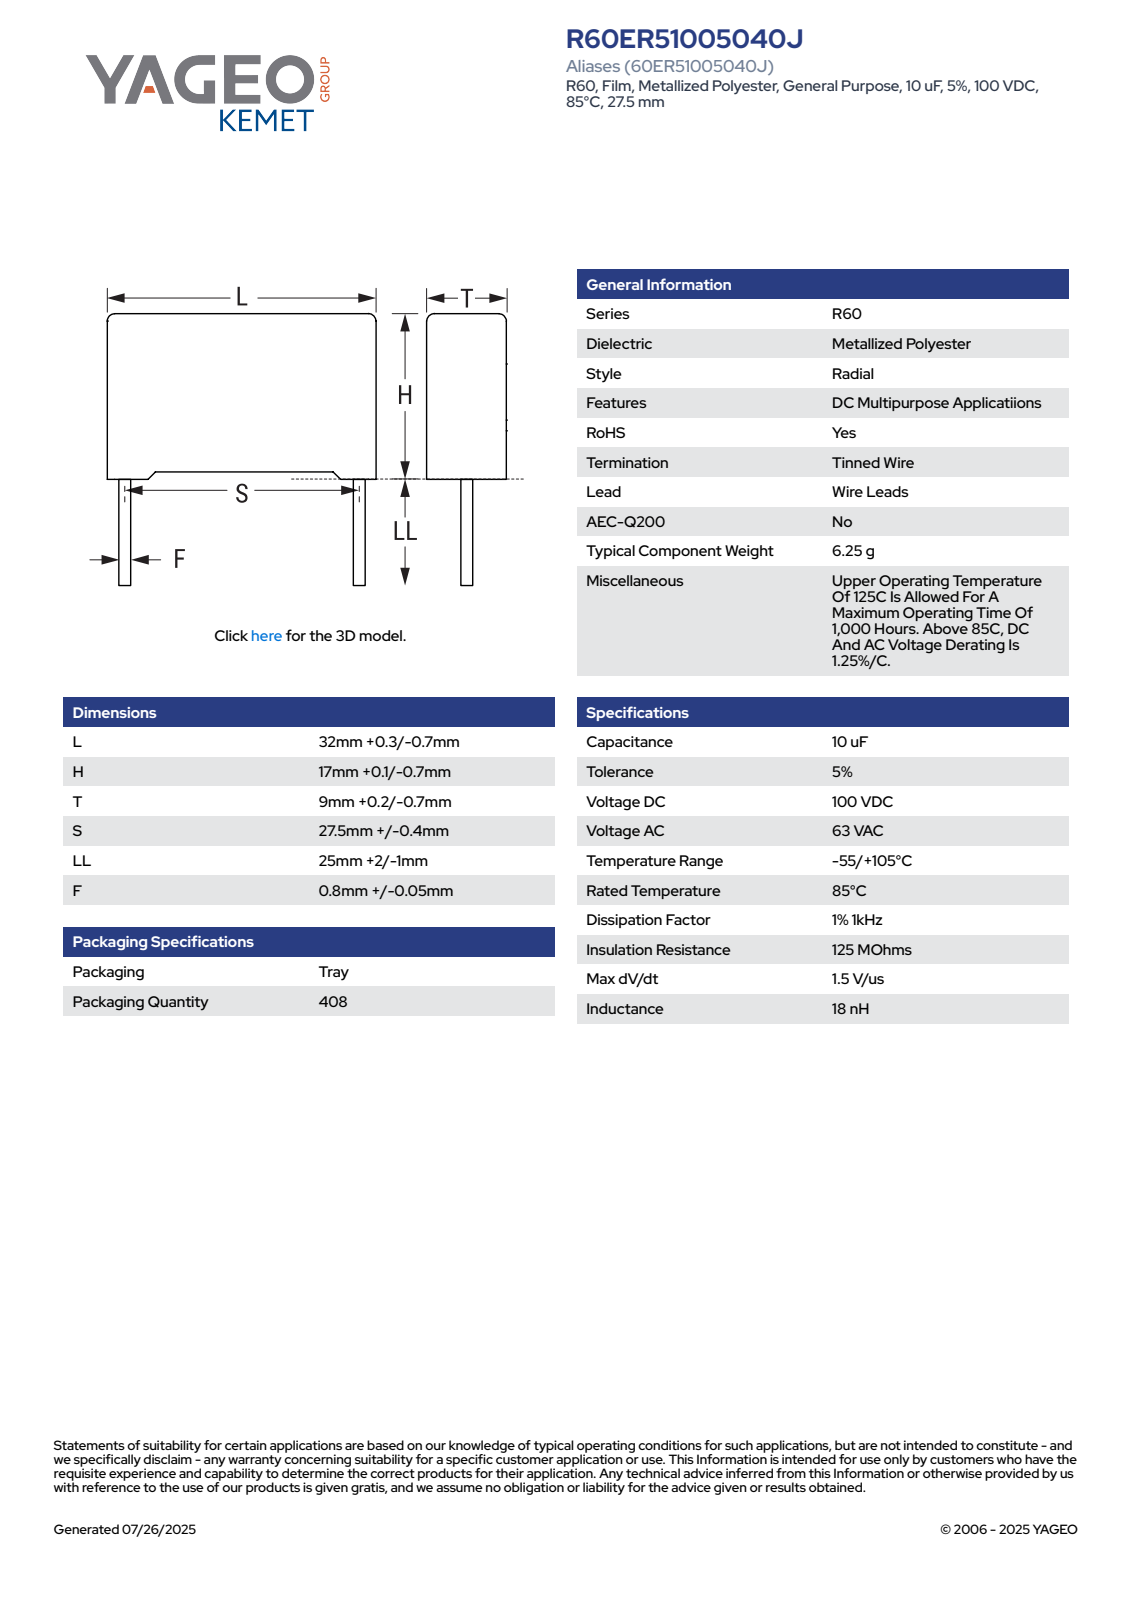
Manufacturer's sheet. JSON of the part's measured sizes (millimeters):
{"part_name": "CFR_RB2_32X17X9_L32.3H17.1T9.2S27.5LL27F0.85", "step_written_by": "SolidWorks 2021 (AUTOMOTIVE_DESIGN)", "units": "millimeters", "bodies": {"solids": 4, "faces": 85, "planar": 77, "cylindrical": 8, "other": 0}, "overall_size": [44.1, 32.3, 9.21], "volume_mm3": 4919, "surface_area_mm2": 2223, "round_bosses_or_shafts": [[0.85, 2]], "partial_cylinders_radius": [[0.5, 4]], "face_to_face_distances": [9.2, 16.35, 32.3, 16.51, 0.59, 0.75, 17.1, 1.08, 9.21, 8.12]}
